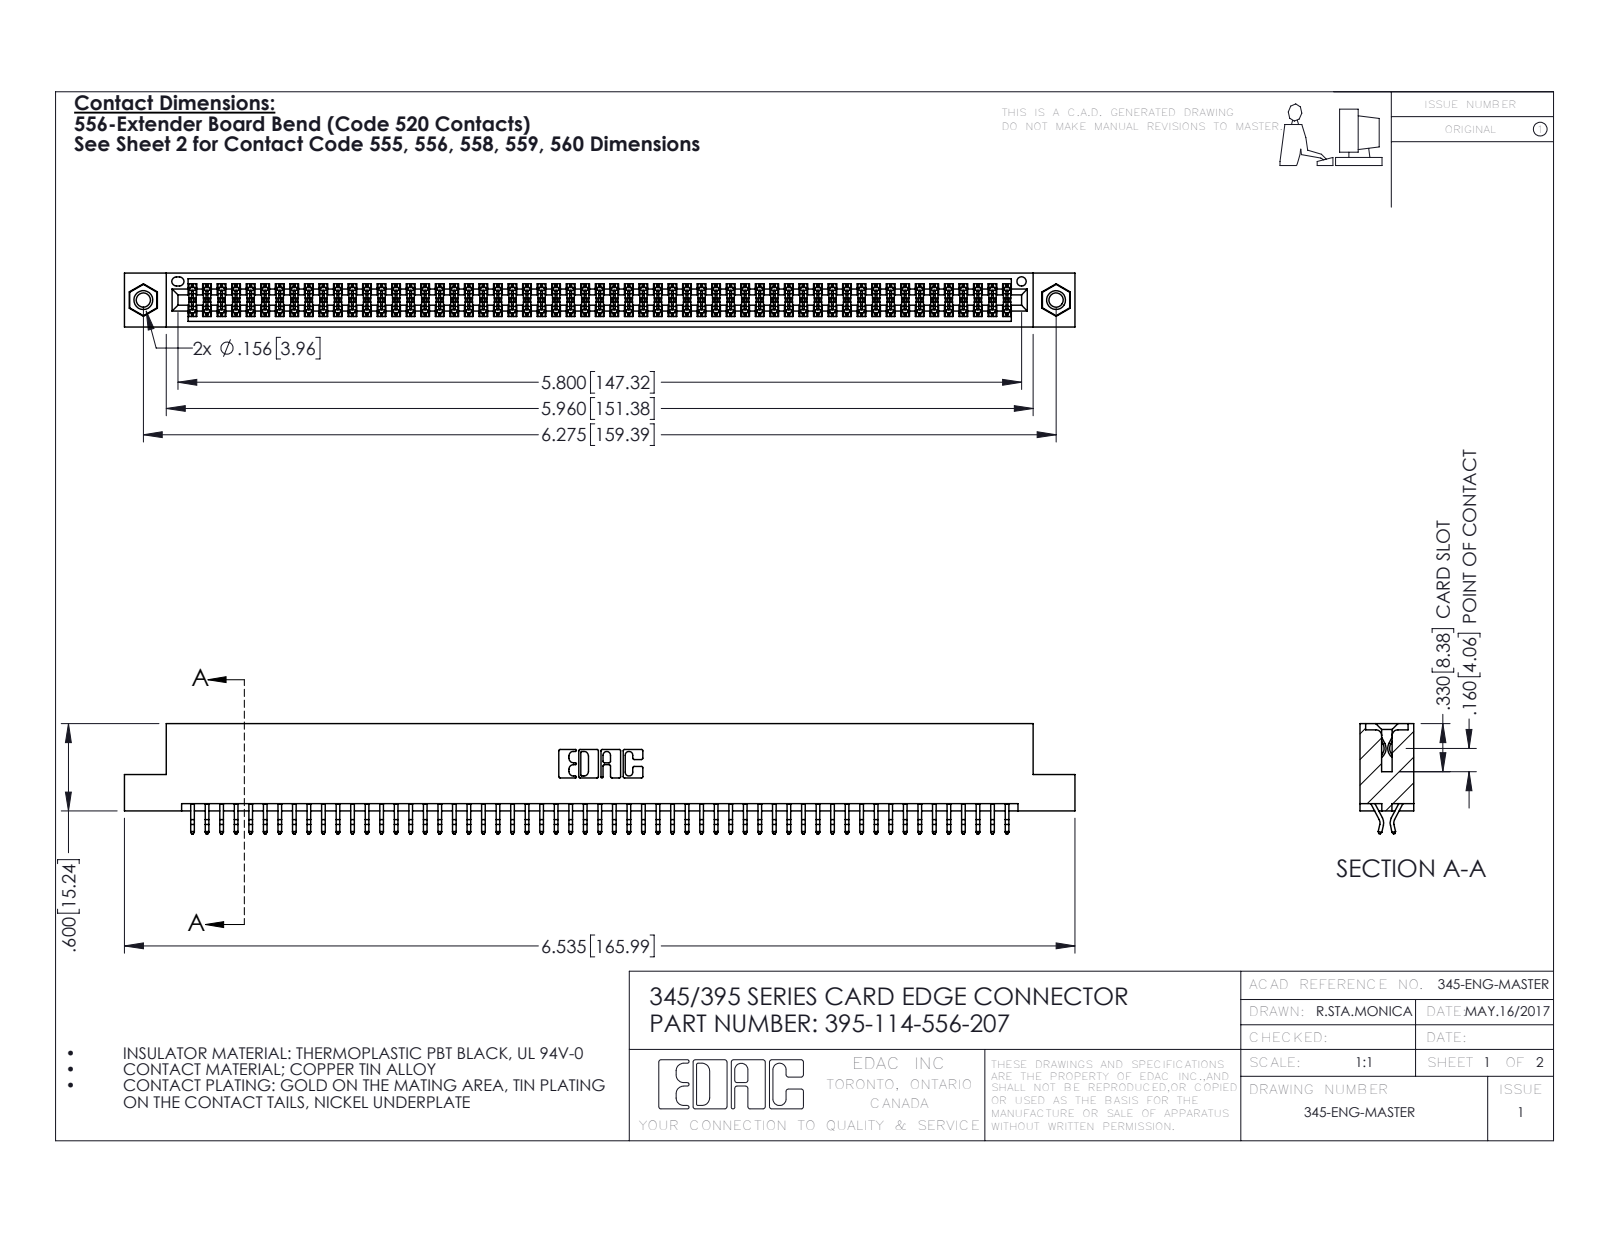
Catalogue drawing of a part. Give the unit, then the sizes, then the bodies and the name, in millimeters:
Units: millimetres
Overall size (bounding box): 166 × 19.2 × 9.4
Round holes (diameter × count): ⌀2.5 ×2, ⌀3.2 ×2, ⌀4 ×2, ⌀1.6 ×1
Round bosses / shafts (diameter × count): ⌀3.9 ×2
Partial cylindrical surfaces — rounded edges, fillets, slot ends (radius × count): R0.2 ×171, R0.3 ×22, R0.2 ×6, R0.8 ×6, R0.7 ×3, R0.3 ×2, R0.4 ×2, R0.5 ×2
Main face-to-face distances: 1.8, 7.6, 9.4, 5.1, 0.6, 2.5, 6.9, 5.7, 4.4, 3.8
Hole centre spacings: 6.9, 153.4, 159.4
Volume: 16 200 mm³ · Surface area: 24 230 mm²
Bodies: 117 solids, 6570 faces (4330 planar, 2224 cylindrical, 16 other)
Part name (STEP PRODUCT): 345 Part_Flush Mounting Lugs - 0.156 Dia-TI; 395-114-556-207; 345-292-001_556 Tail; 345-250-001_345-250-005-103
STEP written by: SolidWorks 2016 (CONFIG_CONTROL_DESIGN)
